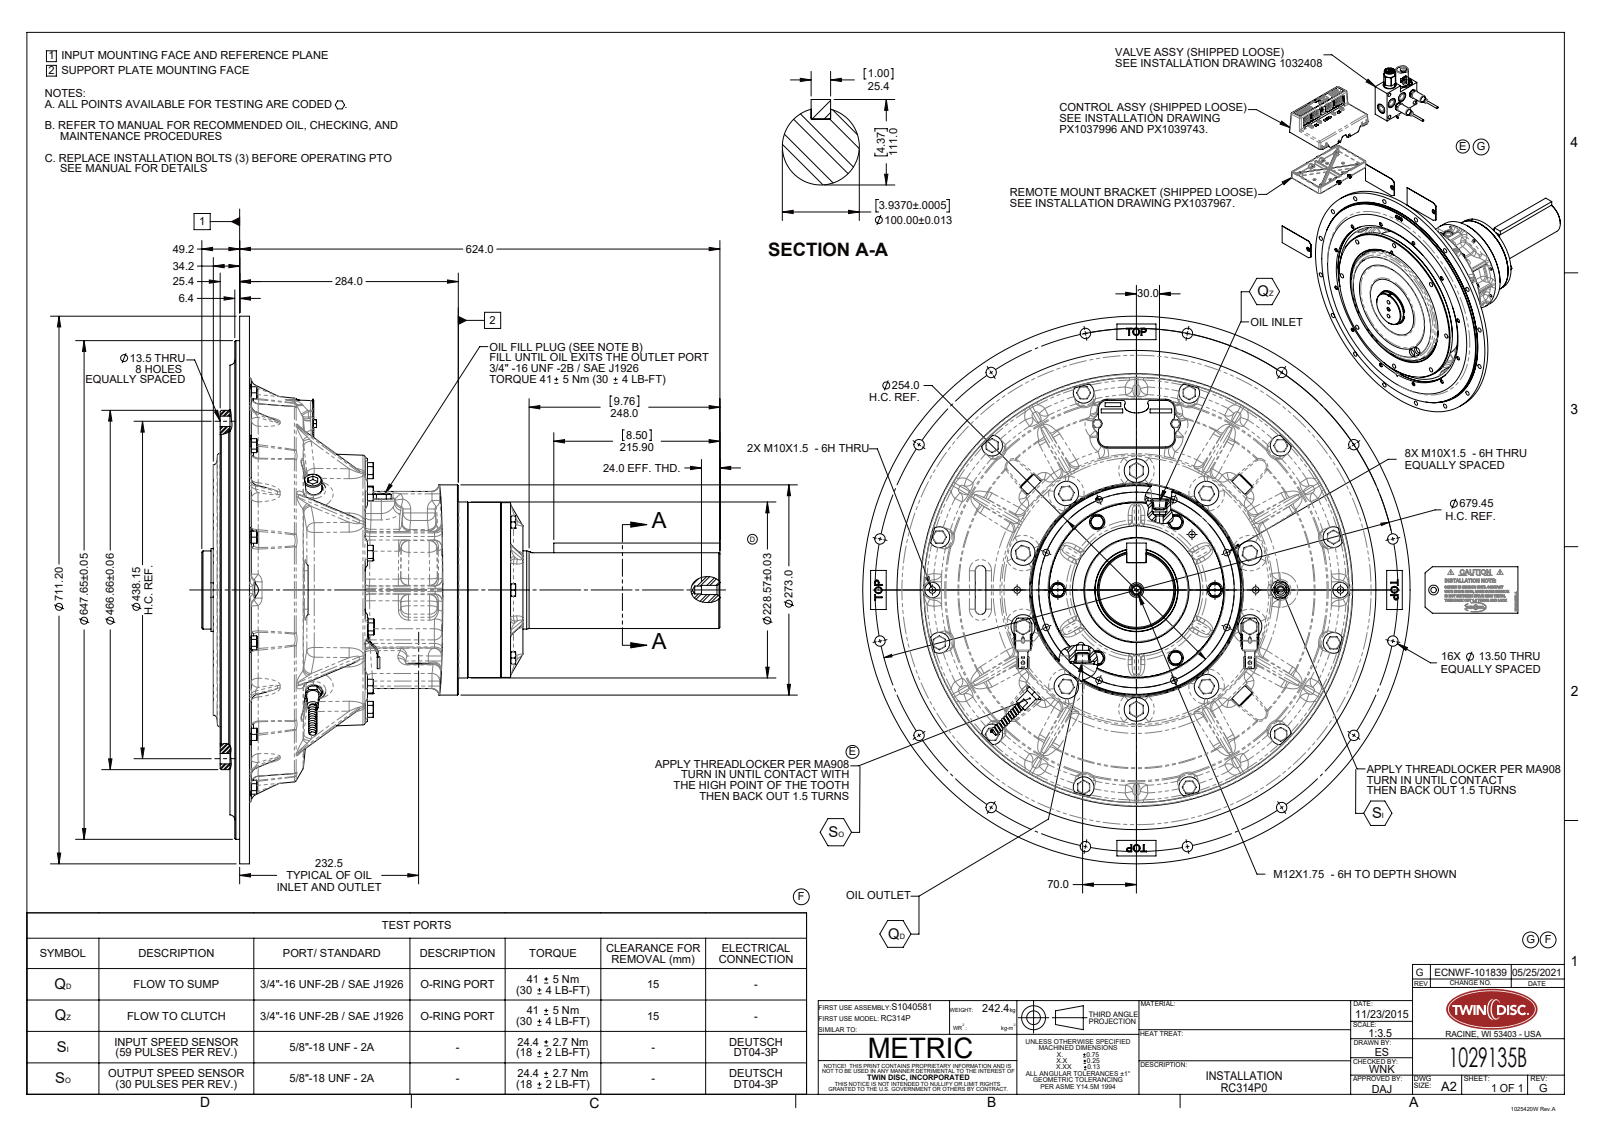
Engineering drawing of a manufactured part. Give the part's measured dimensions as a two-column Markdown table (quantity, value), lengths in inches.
| quantity | value |
| --- | --- |
| part name | 1029135B |
| STEP written by | SolidWorks 2019 (AUTOMOTIVE_DESIGN) |
| units | inches |
| bodies | 0 solids, 2061 faces (590 planar, 367 cylindrical, 1104 other) |
| overall size | 28 × 28 × 26.504 |
| round holes (diameter × count) | 0.531 × 16, 0.335 × 14, 0.437 × 12, 0.531 × 8, 0.472 × 3, 1.188 × 3, 0.187 × 2, 0.75 × 2, 0.787 × 2, 0.875 × 2, 0.425 × 1, 1 × 1 |
| round bosses / shafts (diameter × count) | 0.619 × 3, 0.315 × 2, 28 × 1, 25.51 × 1, 25.498 × 1, 18.373 × 1, 13.658 × 1, 10.866 × 1 |
| partial cylindrical surfaces (radius × count) | 0.394 × 90, 0.118 × 76, 0.197 × 12, 0.531 × 12, 0.06 × 8, 0.5 × 7, 0.689 × 3, 0.01 × 2 |
| main face-to-face distances | 0.1, 0.5, 0.25, 0.75, 1, 0.35, 1.1, 0.4, 0.6, 1.5 |
| hole center spacings | 8.148, 4.439, 13.382, 10.437, 11.506, 3.827, 5, 6.601 |
